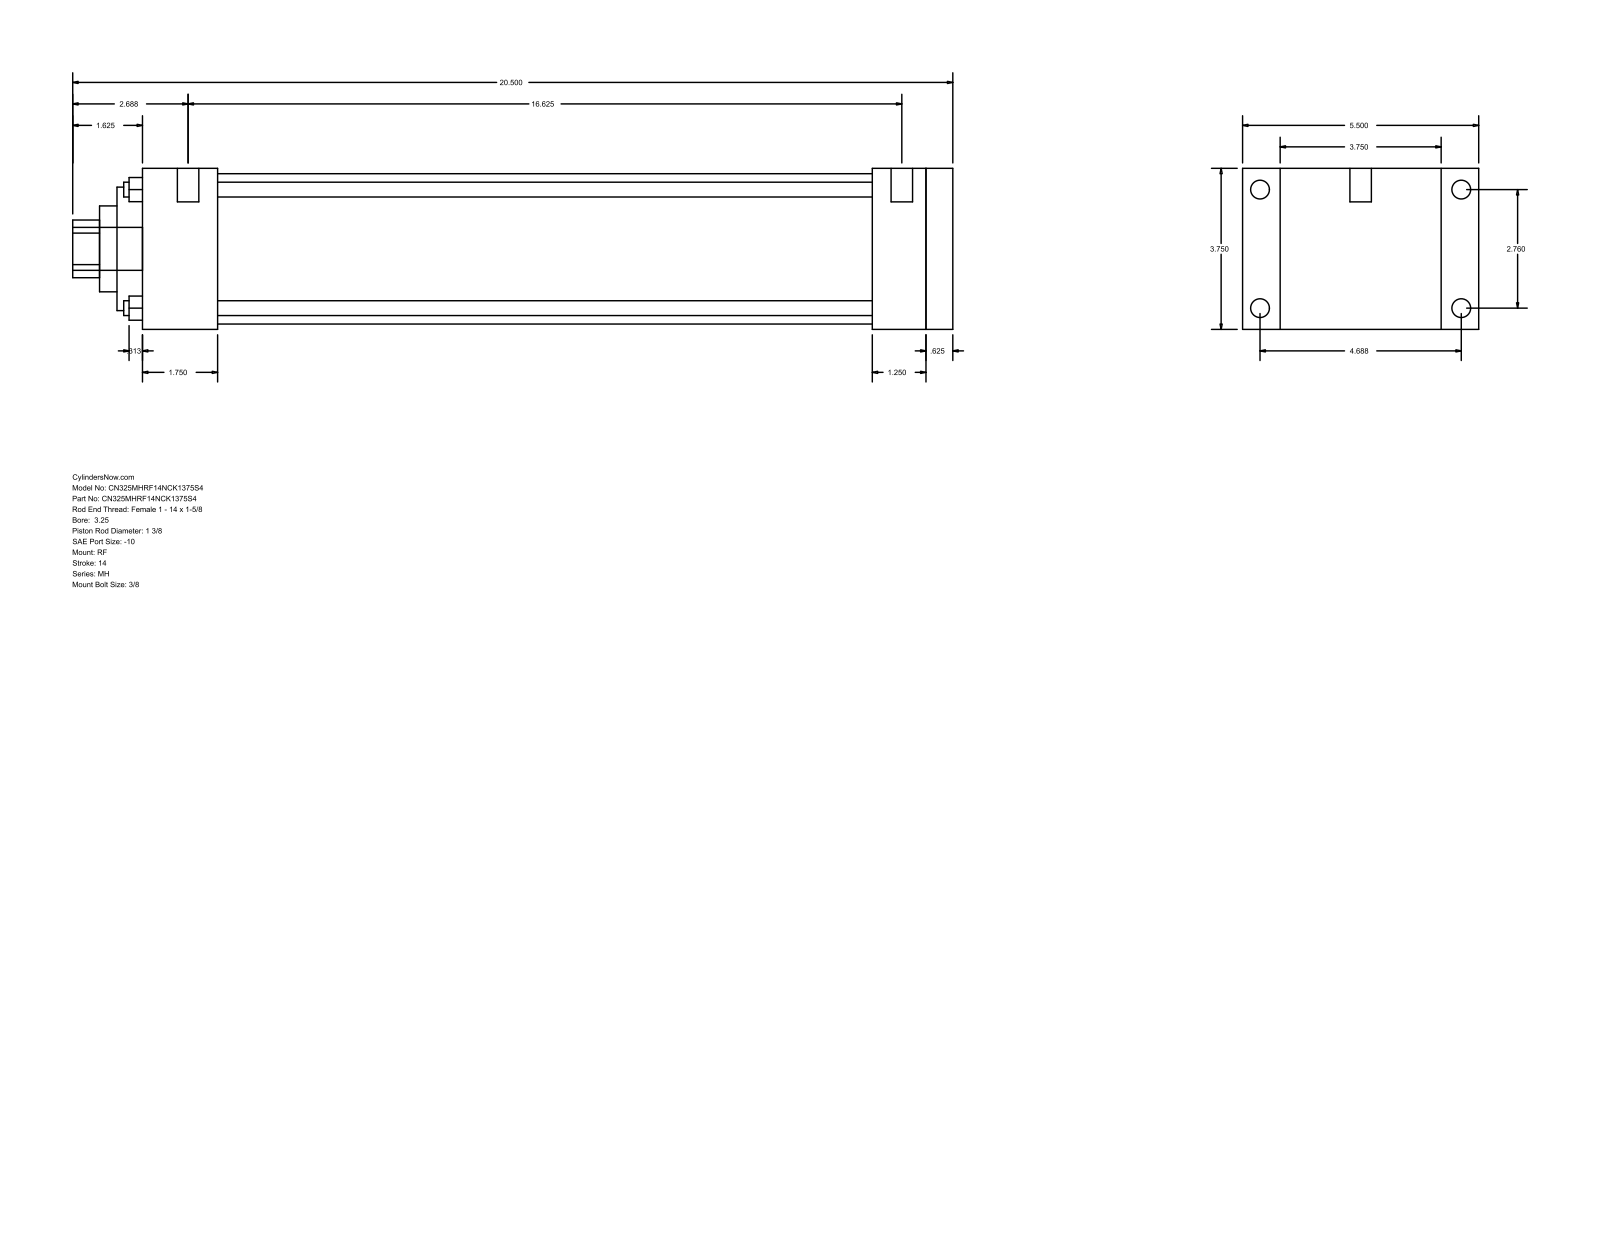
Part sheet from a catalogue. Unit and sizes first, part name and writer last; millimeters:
Units: millimetres
Overall size (bounding box): 520.7 × 139.7 × 95.25
Round holes (diameter × count): ⌀8.76 ×4, ⌀34.92 ×1, ⌀50.8 ×1, ⌀73.03 ×1, ⌀88.9 ×1
Round bosses / shafts (diameter × count): ⌀11.13 ×4, ⌀5.56 ×4, ⌀12.7 ×2, ⌀25.4 ×1
Partial cylindrical surfaces — rounded edges, fillets, slot ends (radius × count): R17.06 ×1
Main face-to-face distances: 95.24, 479.43, 15.88, 463.55, 22.23, 117.47, 44.45, 419.1, 434.98, 431.8
Hole centre spacings: 49.57, 70.1, 99.14
Bodies: 0 solids, 94 faces (65 planar, 29 cylindrical, 0 other)
Part name (STEP PRODUCT): MH_RF__0325_1.375
STEP written by: GSSL Pune (CONFIG_CONTROL_DESIGN)
